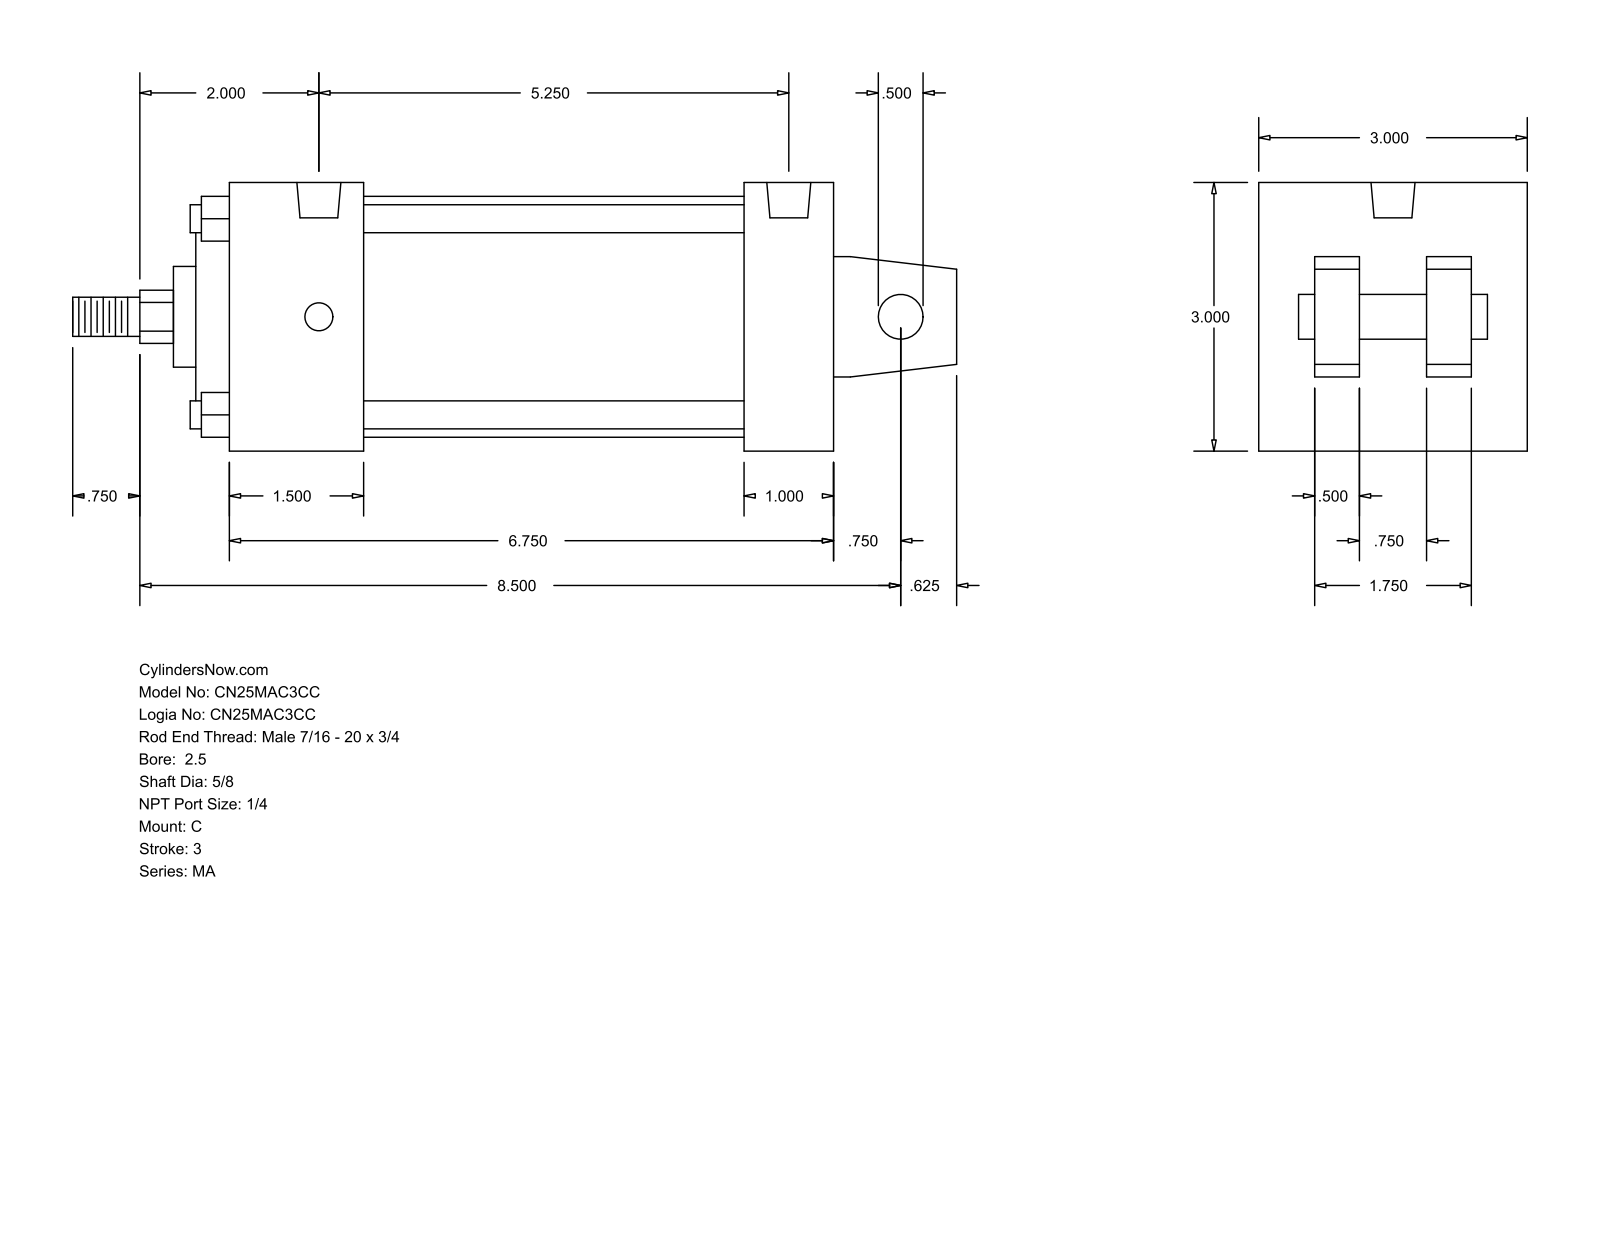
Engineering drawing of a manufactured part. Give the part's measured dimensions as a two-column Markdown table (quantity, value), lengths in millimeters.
| quantity | value |
| --- | --- |
| part name | MA_C__0250_0.625 |
| STEP written by | GSSL Pune (CONFIG_CONTROL_DESIGN) |
| units | millimeters |
| bodies | 0 solids, 105 faces (77 planar, 28 cylindrical, 0 other) |
| overall size | 250.82 × 76.2 × 76.2 |
| round holes (diameter × count) | 7.94 × 4, 12.49 × 2 |
| round bosses / shafts (diameter × count) | 7.94 × 4, 68.33 × 1, 50.8 × 1, 28.57 × 1, 15.88 × 1, 12.7 × 1, 11.11 × 1 |
| partial cylindrical surfaces (radius × count) | 7.54 × 1 |
| main face-to-face distances | 76.2, 171.45, 12.7, 15.87, 60.33, 47.63, 25.4, 38.1, 146.05, 107.95 |
| hole center spacings | 133.35 |
